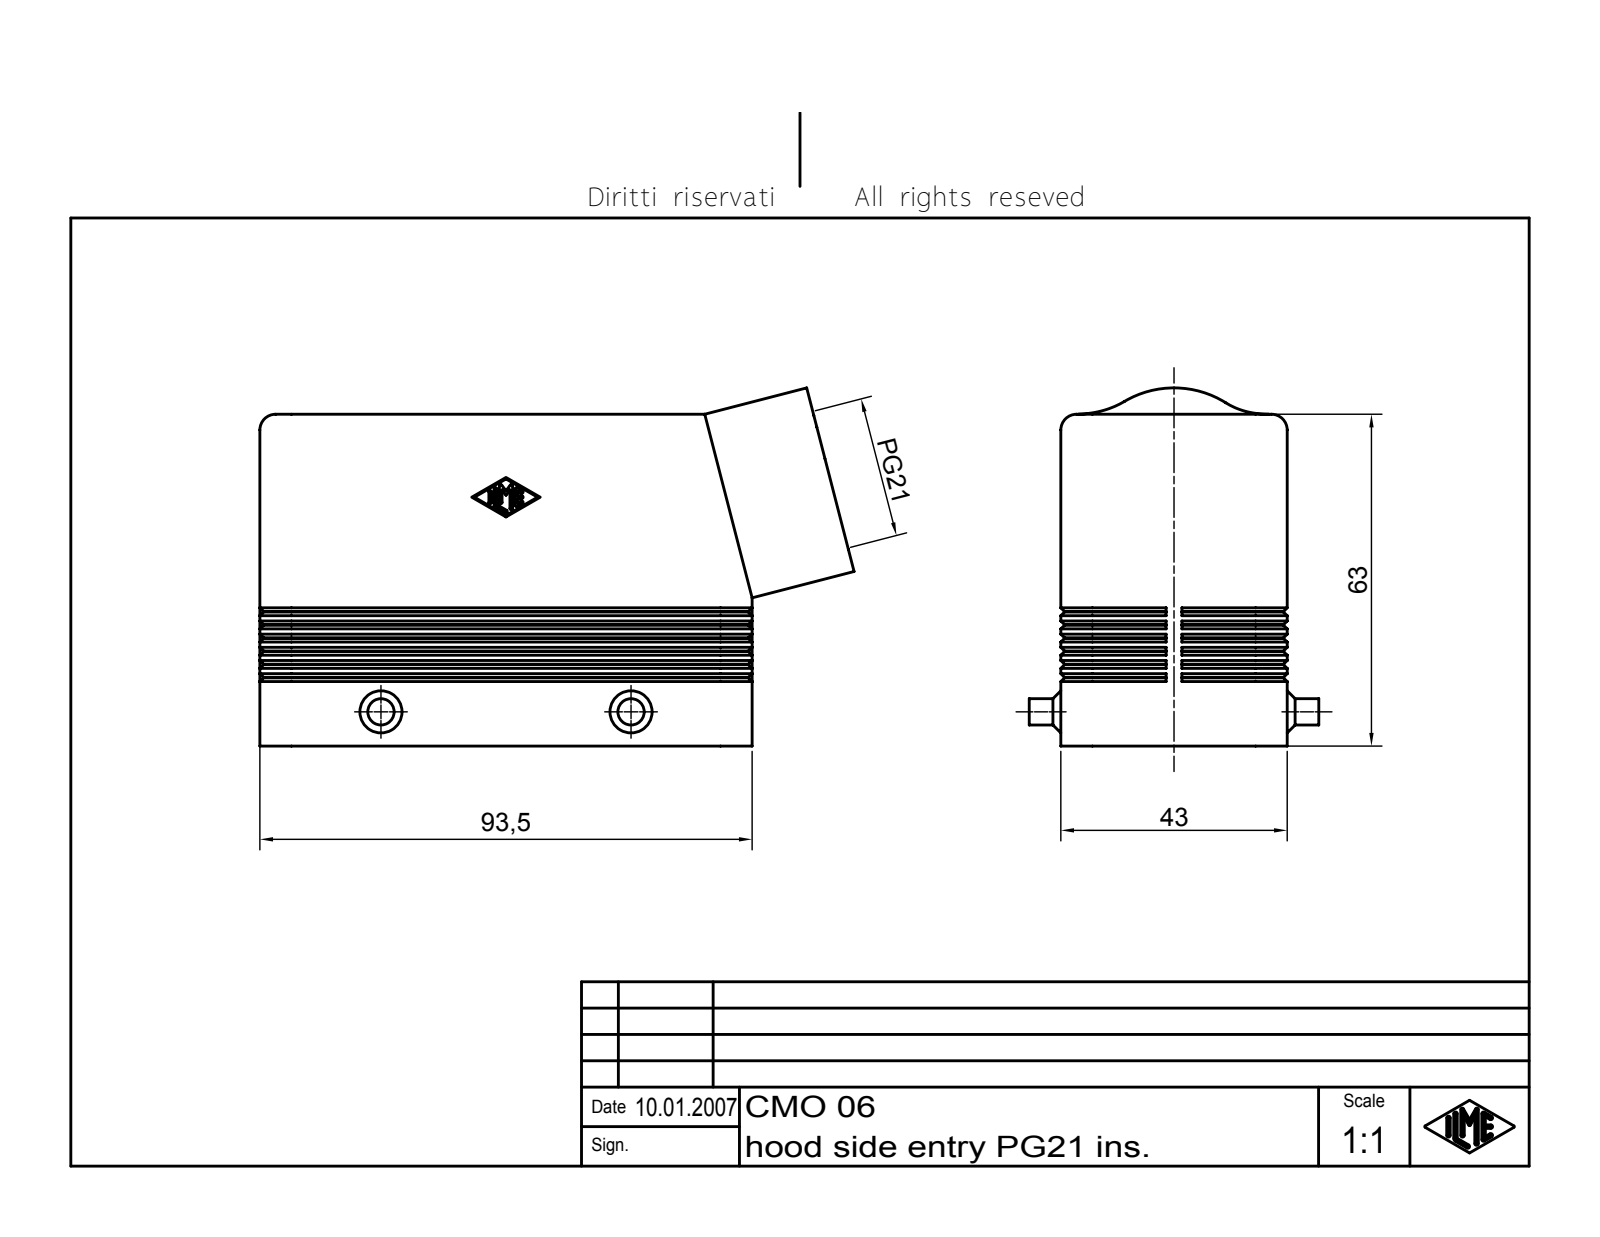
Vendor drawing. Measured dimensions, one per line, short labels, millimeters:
name: CHO Tüllengehäuse 2 Bügel für einen Einsatz
written by: Autodesk Inventor 7 (AUTOMOTIVE_DESIGN)
unit: mm
bodies: 1 solid, 497 faces (184 planar, 113 cylindrical, 200 other)
size: 112.86 × 68 × 55
volume: 80 543 mm³; area: 43 150 mm²
holes: 1× ⌀24.78, 1× ⌀26.78
bosses: 2× ⌀5
rounds: 14× R0.25, 7× R3, 4× R2, 4× R6, 2× R5.3, 1× R1.5
face distances: 3, 40, 37, 43, 8.5, 11.5, 1.77, 79, 82, 90.5
